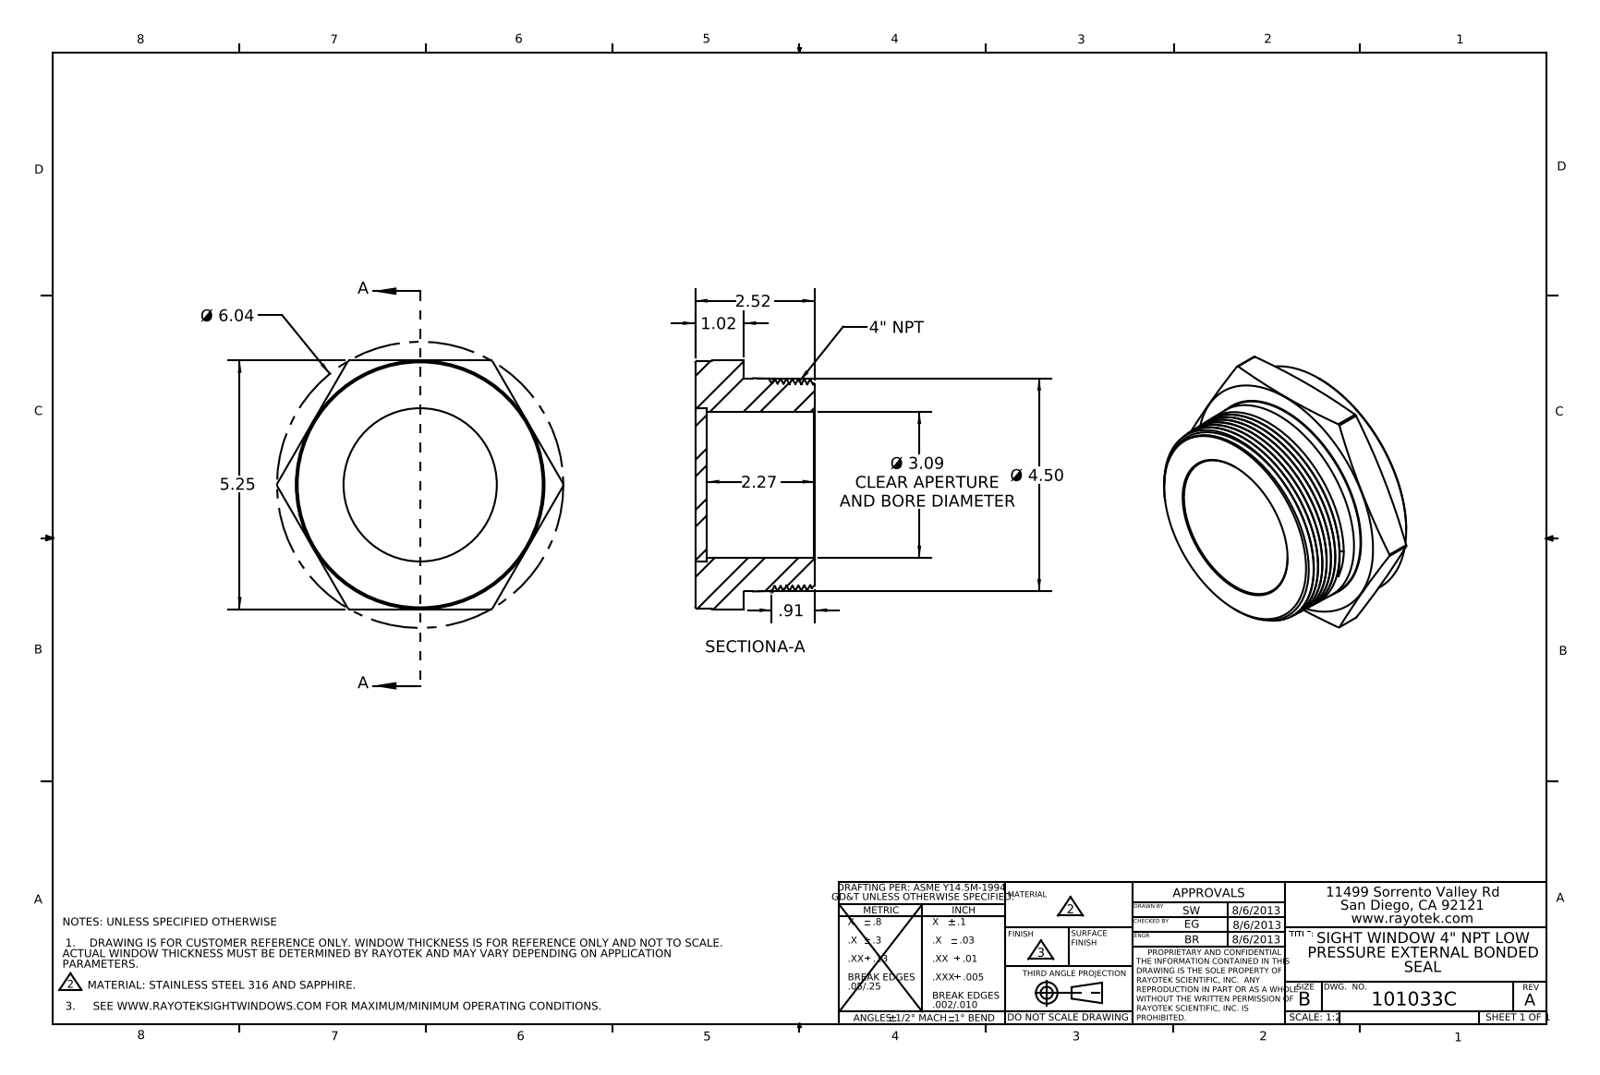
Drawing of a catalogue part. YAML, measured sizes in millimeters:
part_name: "403033"
step_written_by: "SolidWorks 2012 (AUTOMOTIVE_DESIGN)"
units: millimeters
bodies: {solids: 2, faces: 65, planar: 15, cylindrical: 17, other: 33}
overall_size: [153.5, 133.4, 64]
volume: 479000
surface_area: 79290
round_holes:
  - {diameter: 78.5, count: 1}
  - {diameter: 82.1, count: 1}
round_bosses_or_shafts:
  - {diameter: 132.8, count: 1}
  - {diameter: 114.3, count: 1}
partial_cylinders:
  - {radius: 76.7, count: 1}
face_to_face_distances: [6.2, 64, 57.8, 133.4, 25.9, 19.7, 38.1]
